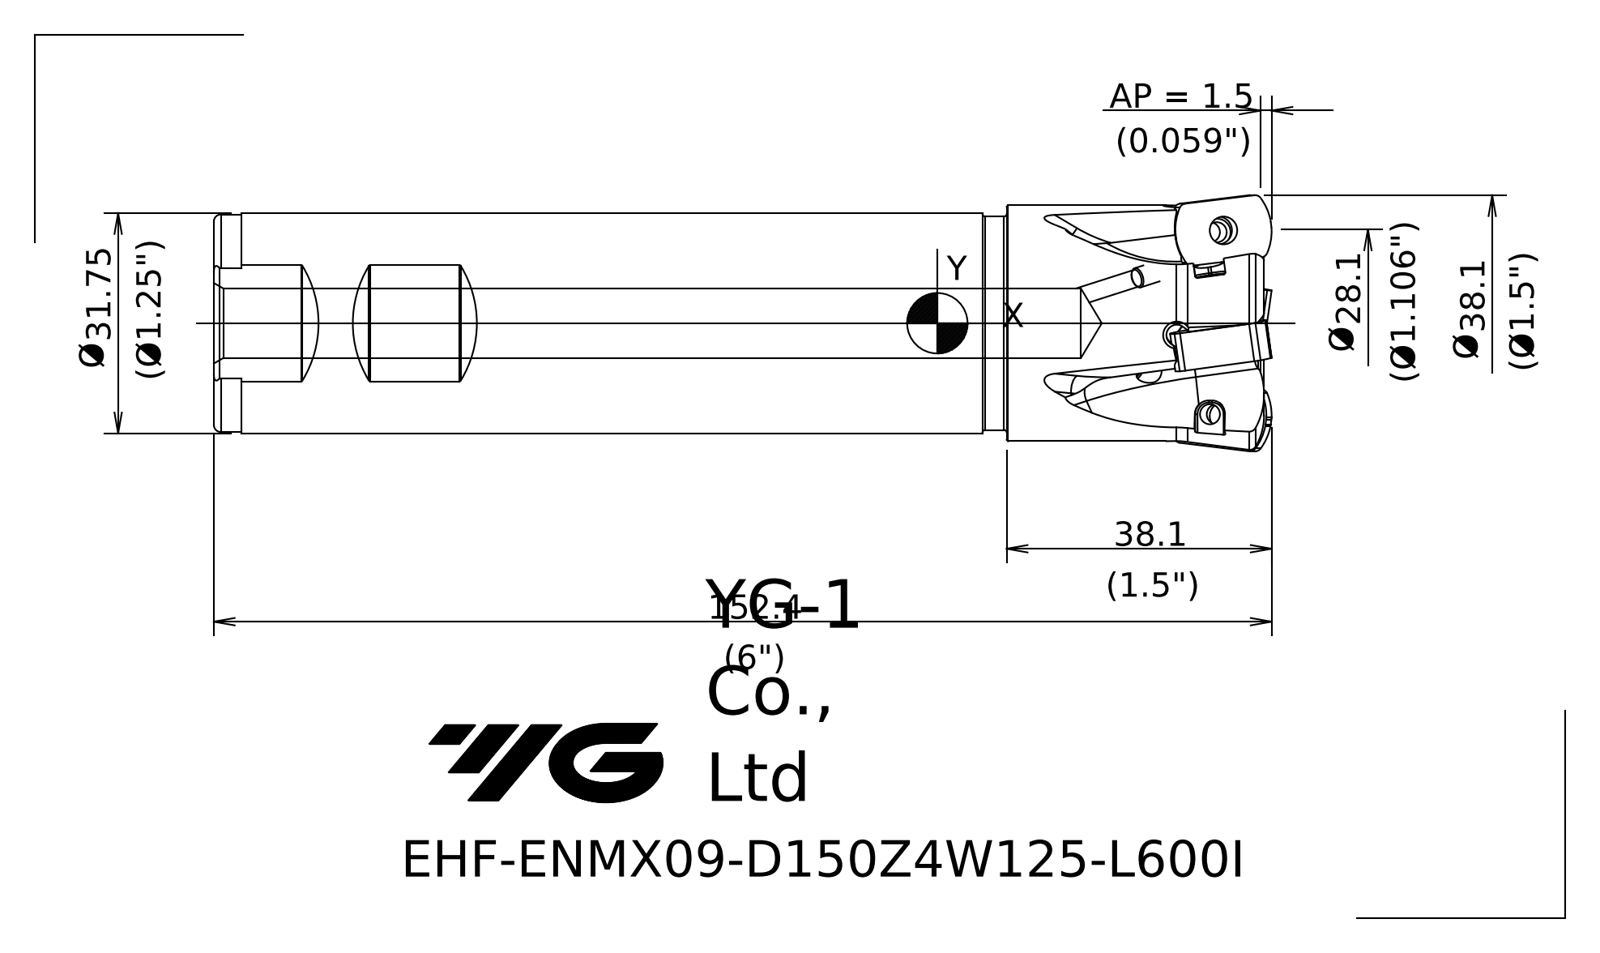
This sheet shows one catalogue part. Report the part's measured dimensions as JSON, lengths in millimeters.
{"part_name": "120185C07CB1h82k", "step_written_by": "SIEMENS PLM Software NX 10.0 (AP203_CONFIGURATION_CONTROLLED_3D_DESIGN_OF_MECHANICAL_PARTS_AND_ASSEMBLIES_MIM_LF)", "units": "millimeters", "bodies": {"solids": 1, "faces": 57, "planar": 12, "cylindrical": 9, "other": 36}, "overall_size": [152.42, 38.11, 38.11], "volume_mm3": 115398, "surface_area_mm2": 21487, "round_holes": [[1.5, 1], [10, 1]], "round_bosses_or_shafts": [[34, 1], [31.75, 1], [31.35, 1], [30.75, 1]], "partial_cylinders_radius": [[0.3, 3]], "face_to_face_distances": [150.43, 36.13, 114.3, 16.13, 24.55, 8.42, 146.43, 110.3, 4, 39.63]}
